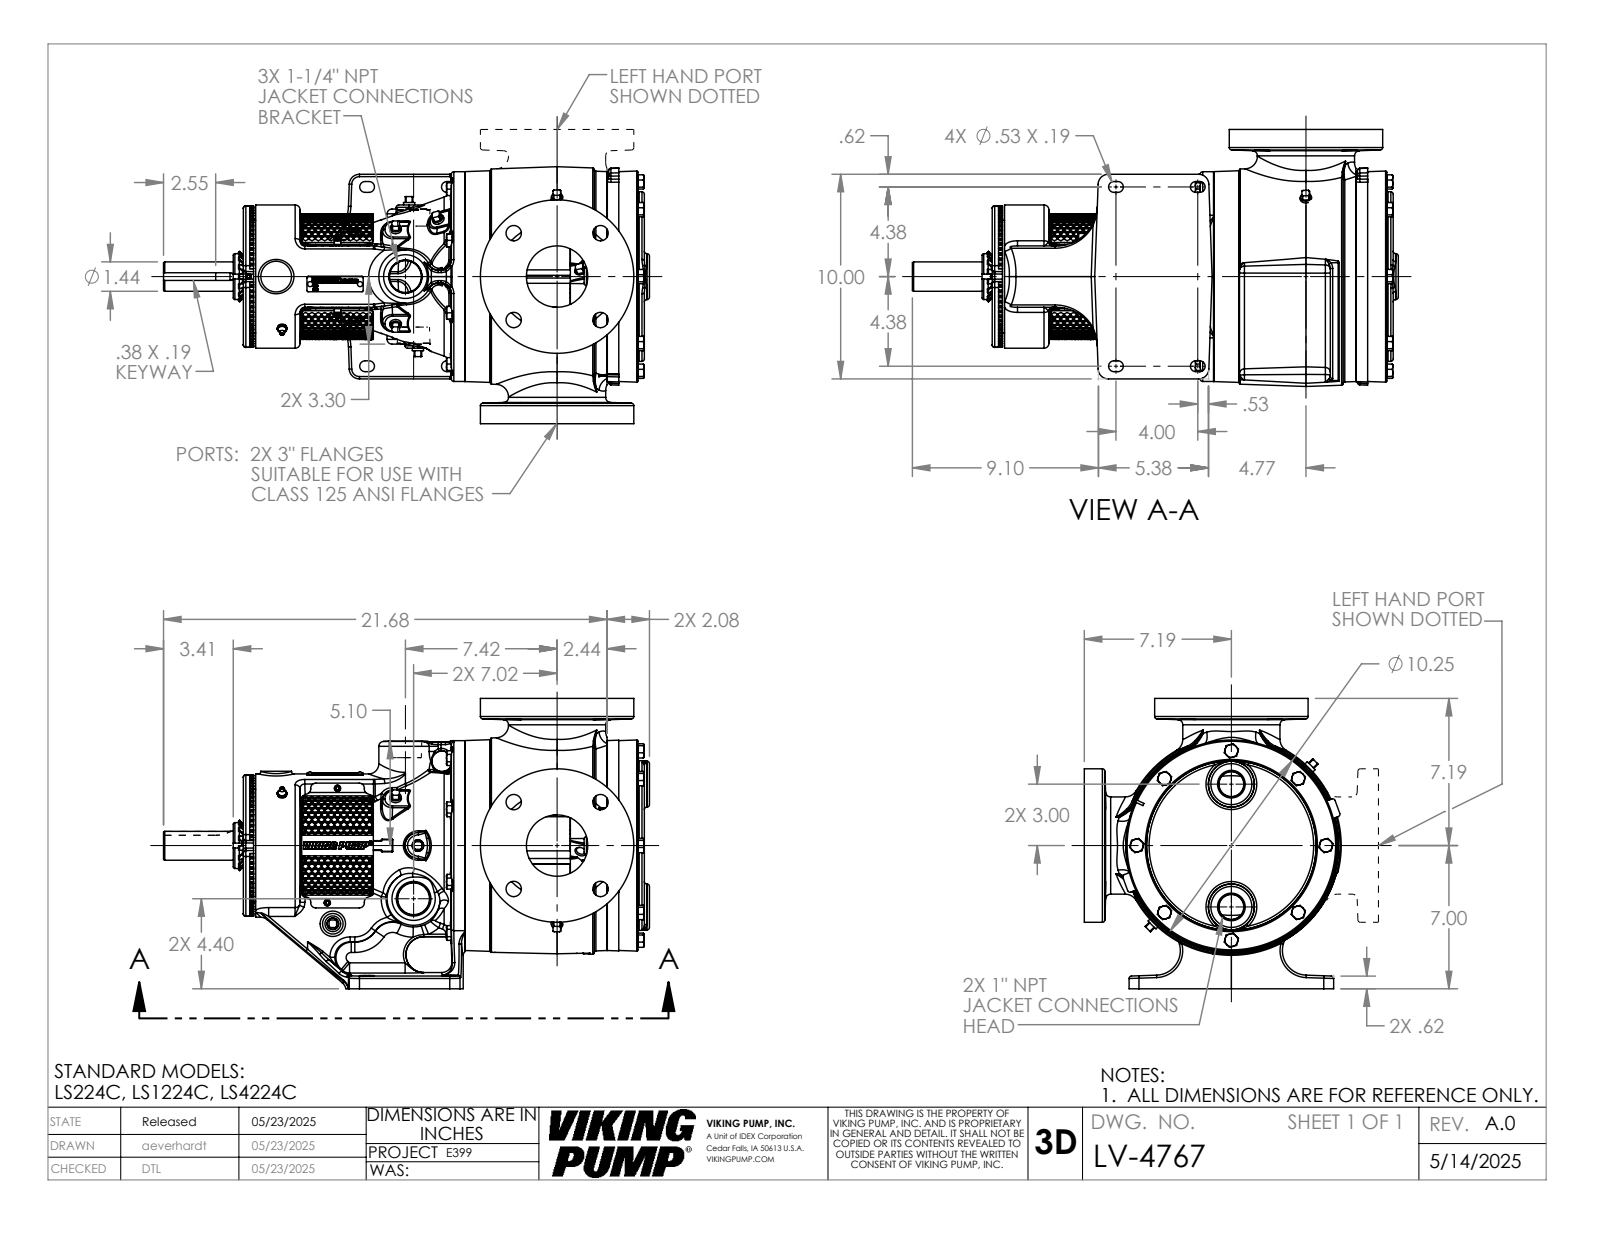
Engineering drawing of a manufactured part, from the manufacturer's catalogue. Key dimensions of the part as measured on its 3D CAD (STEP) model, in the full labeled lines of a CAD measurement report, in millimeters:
Part name (STEP PRODUCT): LV-4767
STEP written by: SolidWorks 2024 (AUTOMOTIVE_DESIGN)
Units: millimetres
Bodies: 1 solid, 4011 faces (1316 planar, 748 cylindrical, 1947 other)
Overall size (bounding box): 603.4 × 360.4 × 319
Volume: 20 400 000 mm³ · Surface area: 924 500 mm²
Round holes (diameter × count): ⌀19.1 ×8, ⌀27.8 ×8, ⌀5.1 ×6, ⌀6.4 ×5, ⌀4 ×3, ⌀6.8 ×2, ⌀8 ×2, ⌀38.3 ×1, ⌀40.1 ×1, ⌀40.5 ×1, ⌀46.5 ×1, ⌀62 ×1
Round bosses / shafts (diameter × count): ⌀15.9 ×10, ⌀15.9 ×6, ⌀11.1 ×3, ⌀7.9 ×3, ⌀190.5 ×2, ⌀120.7 ×2, ⌀260.4 ×1, ⌀177.8 ×1
Partial cylindrical surfaces — rounded edges, fillets, slot ends (radius × count): R1.6 ×109, R1.8 ×74, R3 ×62, R12.7 ×26, R0.8 ×18, R6.1 ×16, R6.4 ×12, R6 ×8
Main face-to-face distances: 360.4, 7.9, 38.1, 12.7, 420.2, 428.1, 57.2, 89.8, 330.5, 338.3
Hole centre spacings: 107.8, 76.2, 34.9, 55.4, 112.9, 117.5, 162.7, 166.1
